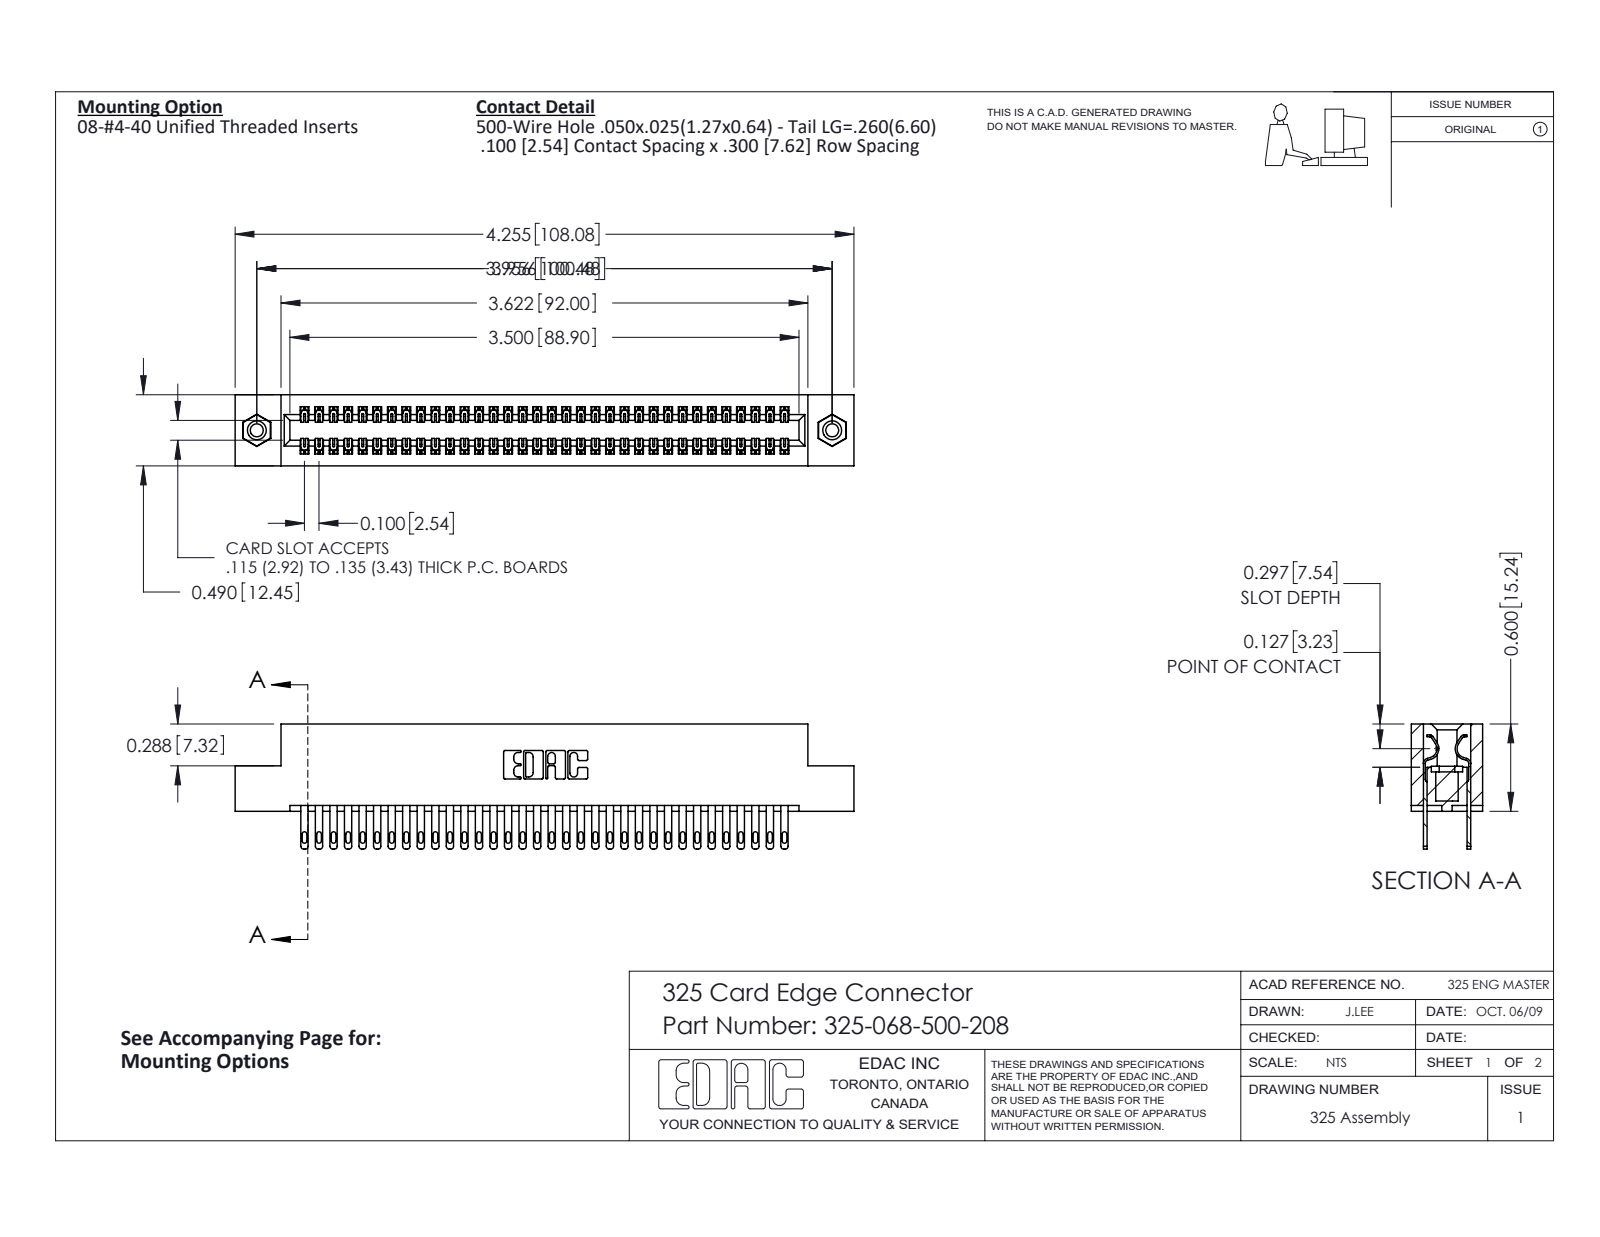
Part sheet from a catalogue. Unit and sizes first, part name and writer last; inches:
Units: inches
Overall size (bounding box): 4.255 × 0.86 × 0.49
Round holes (diameter × count): ⌀0.089 ×2, ⌀0.125 ×2, ⌀0.16 ×2
Round bosses / shafts (diameter × count): ⌀0.155 ×2
Partial cylindrical surfaces — rounded edges, fillets, slot ends (radius × count): R0.006 ×102, R0.016 ×68, R0.02 ×68, R0.01 ×22, R0.007 ×6, R0.031 ×6, R0.026 ×3, R0.014 ×2
Main face-to-face distances: 0.083, 0.407, 0.3, 0.107, 0.383, 0.025, 0.49, 0.325, 0.275, 0.04
Hole centre spacings: 3.956
Volume: 0.859 in³ · Surface area: 27.25 in²
Bodies: 71 solids, 3438 faces (2142 planar, 1280 cylindrical, 16 other)
Part name (STEP PRODUCT): 325-068-500-208; 325-292-001_325-293-100; 325 Part_TI; 345-250-001_345-250-003-102
STEP written by: SolidWorks 2016 (CONFIG_CONTROL_DESIGN)
